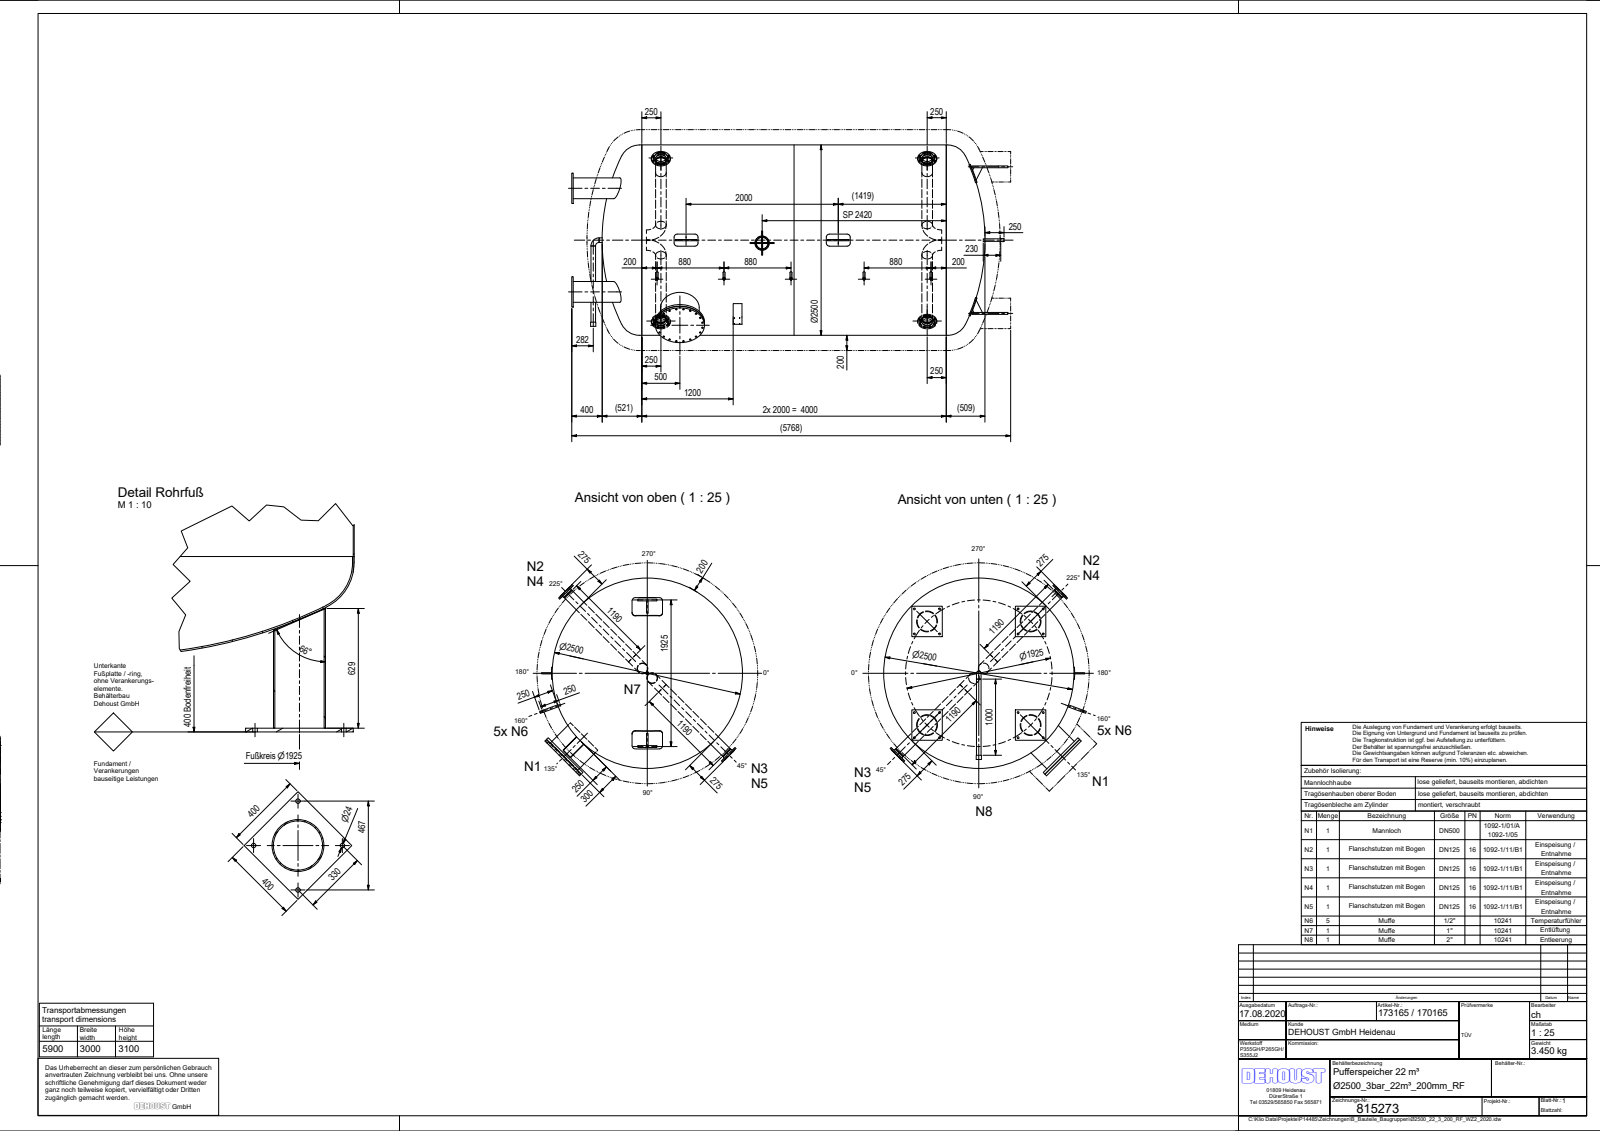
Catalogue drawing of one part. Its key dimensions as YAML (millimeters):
part_name: "Ø2500_22_3_200_RF_WZ2_2020; Klöpper_Gew_Ø2500_5,5; Klöpper_Gew_Ø2500_8,3; Zyl_Ø2500_5x4000_2020 (+8 more)"
step_written_by: "Autodesk Inventor 2019 (AUTOMOTIVE_DESIGN)"
units: millimeters
bodies: {solids: 54, faces: 429, planar: 182, cylindrical: 221, other: 26}
overall_size: [5732.1, 2664.05, 2595.98]
volume: 413400000
surface_area: 104700000
round_holes:
  - {diameter: 22, count: 40}
  - {diameter: 18, count: 32}
  - {diameter: 24, count: 16}
  - {diameter: 131.7, count: 8}
  - {diameter: 18.63, count: 5}
  - {diameter: 21.7, count: 5}
  - {diameter: 26.9, count: 5}
  - {diameter: 5.8, count: 4}
  - {diameter: 139.7, count: 4}
  - {diameter: 258.8, count: 4}
  - {diameter: 5, count: 2}
  - {diameter: 52.3, count: 2}
round_bosses_or_shafts:
  - {diameter: 139.7, count: 8}
  - {diameter: 26.9, count: 5}
  - {diameter: 26.4, count: 5}
  - {diameter: 273, count: 4}
  - {diameter: 250, count: 4}
  - {diameter: 188, count: 4}
  - {diameter: 645, count: 2}
  - {diameter: 2500, count: 1}
partial_cylinders:
  - {radius: 42, count: 16}
  - {radius: 6, count: 8}
  - {radius: 5, count: 2}
  - {radius: 10, count: 2}
  - {radius: 36, count: 2}
  - {radius: 72, count: 2}
  - {radius: 125, count: 1}
  - {radius: 1259, count: 1}
face_to_face_distances: [20, 2808.97, 3093.97, 2788.97, 3073.97, 285, 600, 27.99, 25, 650]
hole_center_spacings: [105, 300, 93.86, 185.41, 352.67, 3500, 485.41, 194.02]
